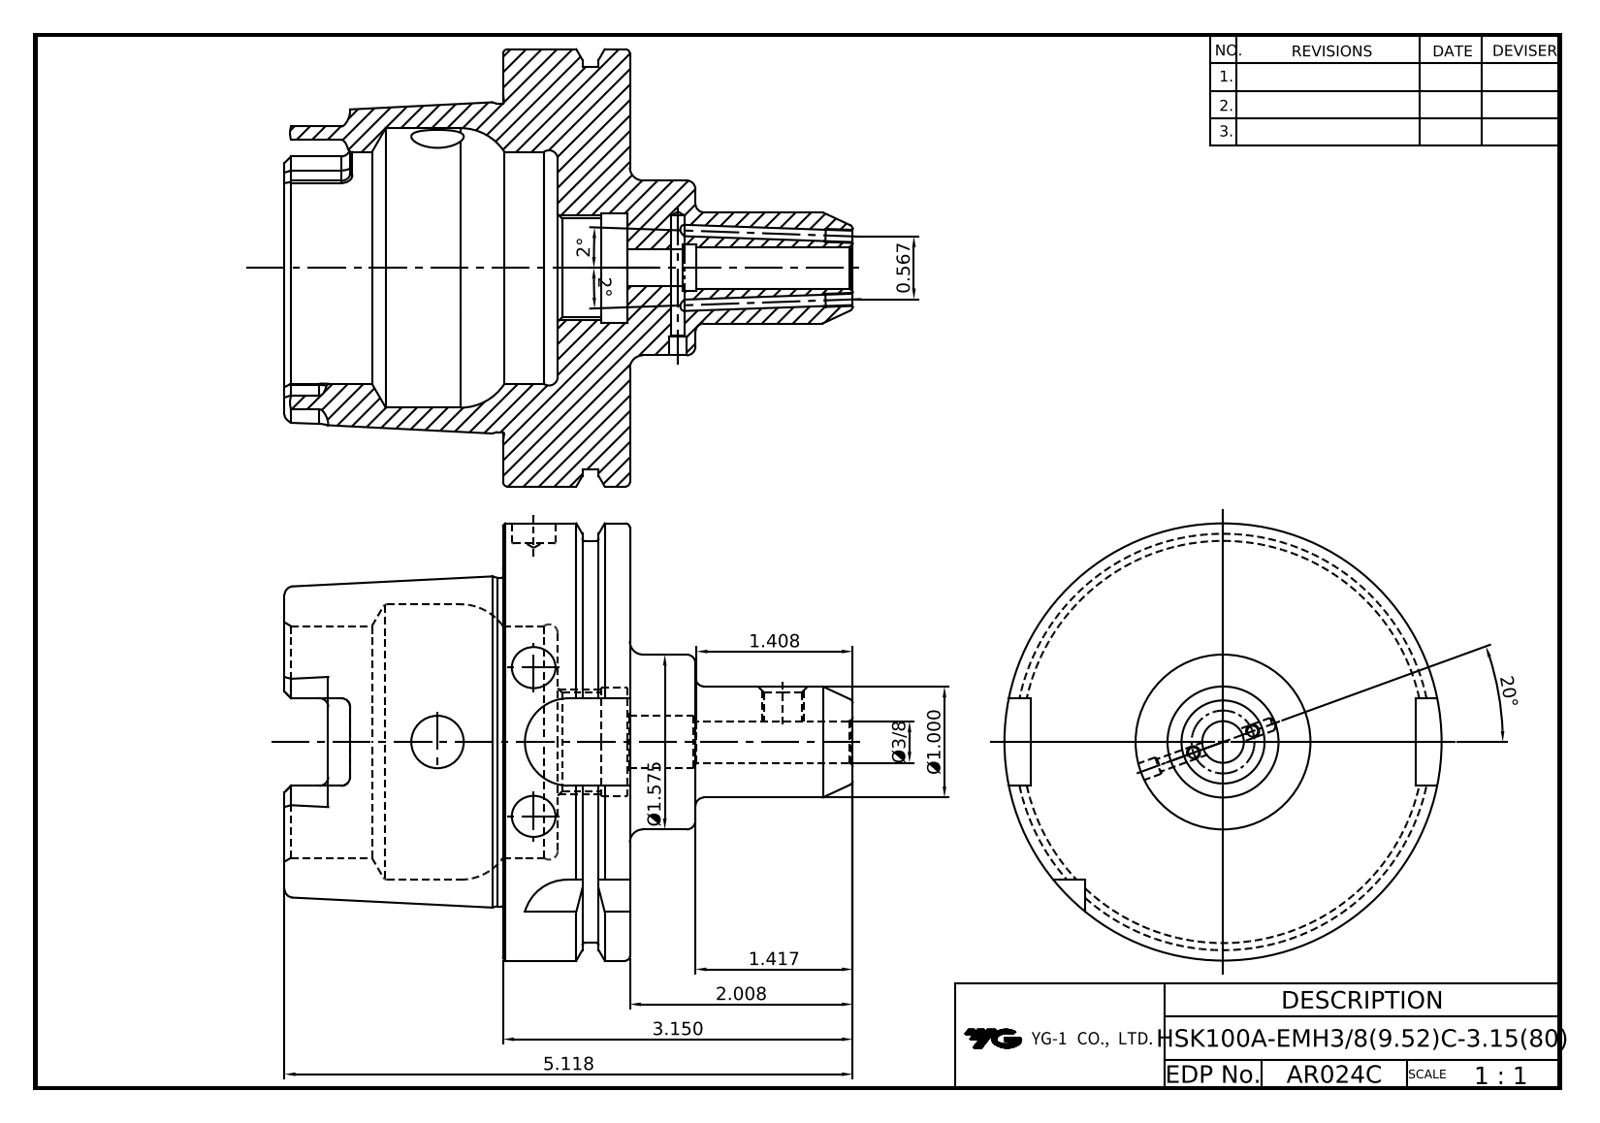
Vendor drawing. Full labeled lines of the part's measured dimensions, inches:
Part name (STEP PRODUCT): LO-HSK100A-EMH9.525C-80
STEP written by: Autodesk Inventor 2022 (AUTOMOTIVE_DESIGN)
Units: inches
Bodies: 1 solid, 134 faces (39 planar, 42 cylindrical, 53 other)
Overall size (bounding box): 5.118 × 3.937 × 3.937
Volume: 17.38 in³ · Surface area: 87.36 in²
Round holes (diameter × count): ⌀0.394 ×3, ⌀0.097 ×2, ⌀0.472 ×2, ⌀0.118 ×1, ⌀0.157 ×1, ⌀0.33 ×1, ⌀0.375 ×1, ⌀0.881 ×1, ⌀0.984 ×1, ⌀2.087 ×1, ⌀2.48 ×1
Round bosses / shafts (diameter × count): ⌀3.937 ×1, ⌀3.622 ×1, ⌀2.969 ×1, ⌀1.575 ×1, ⌀1 ×1
Partial cylindrical surfaces — rounded edges, fillets, slot ends (radius × count): R0.079 ×6, R0.192 ×4, R0.394 ×4
Main face-to-face distances: 1.142, 0.492, 0.65, 3.11, 2.461, 1.969, 0.591, 3.465, 3.091, 1.122
Hole centre spacings: 1.299, 2.244
